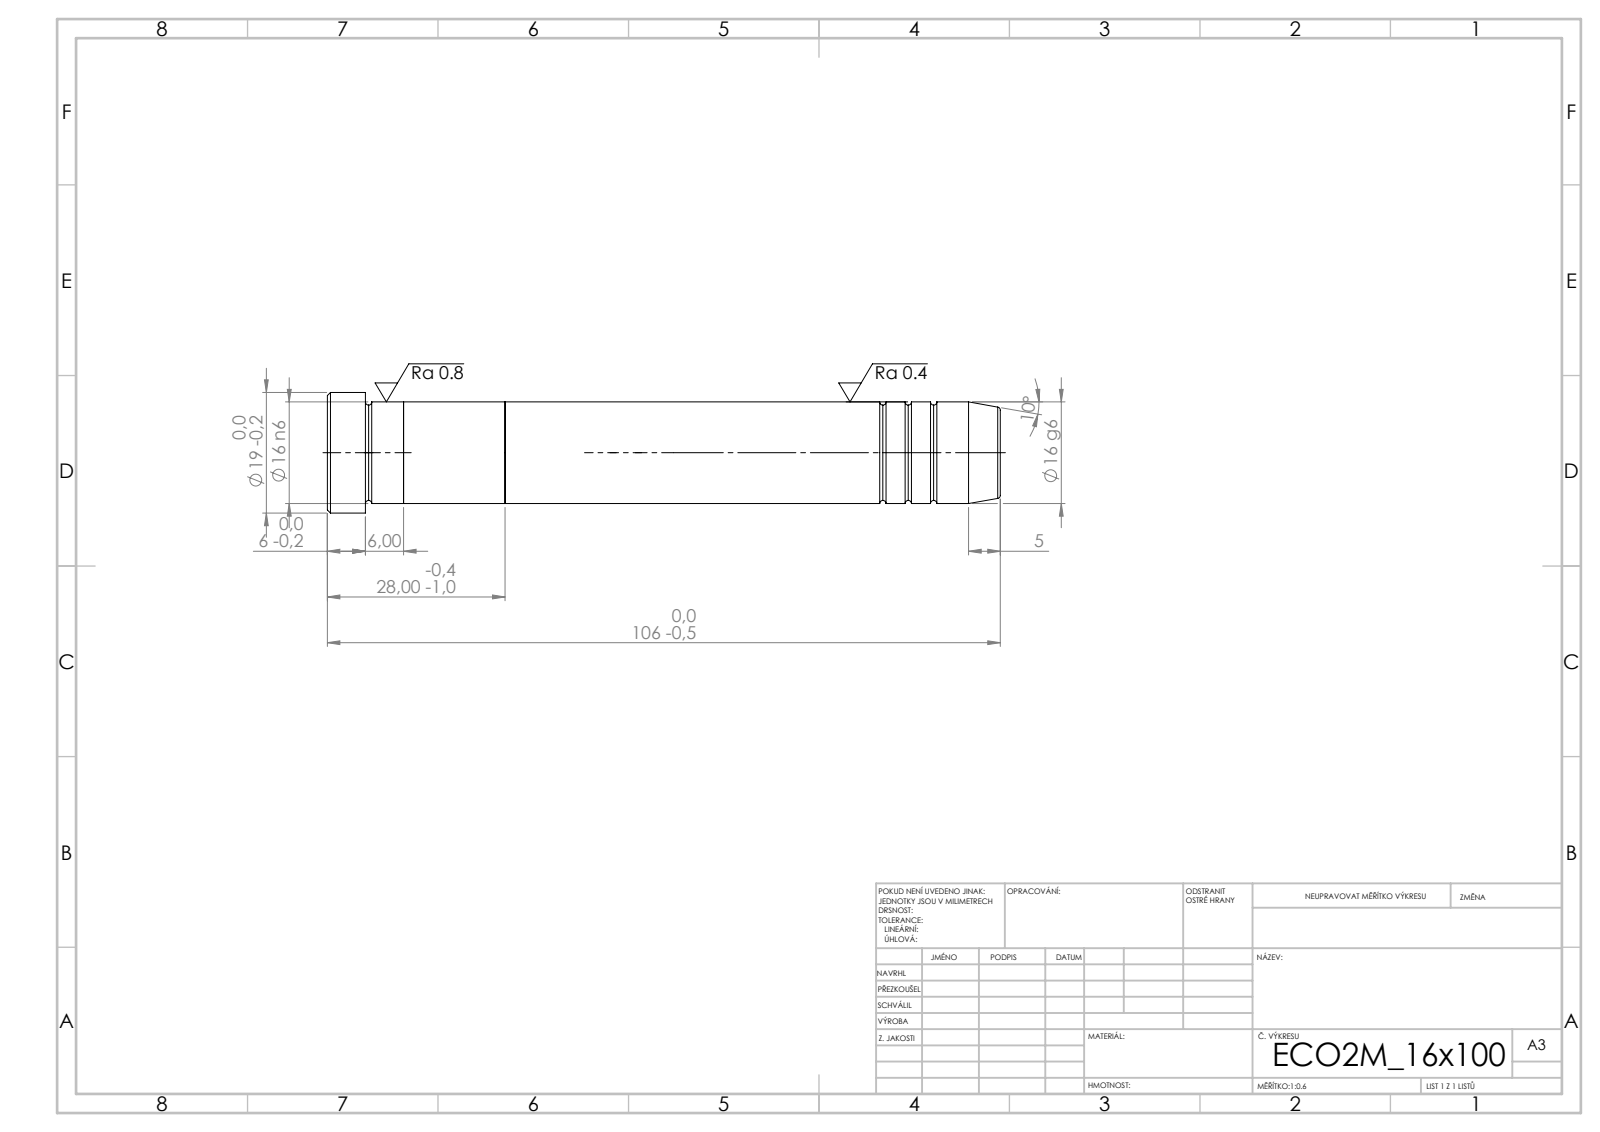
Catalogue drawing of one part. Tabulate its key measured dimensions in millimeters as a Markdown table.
| quantity | value |
| --- | --- |
| STEP written by | SolidWorks 2019 (CONFIG_CONTROL_DESIGN) |
| units | millimeters |
| bodies | 3 solids, 43 faces (7 planar, 14 cylindrical, 22 other) |
| overall size | 106 × 19 × 19 |
| volume | 21 615 mm³ |
| surface area | 6 782 mm² |
| round bosses / shafts (diameter × count) | 19 × 1, 16 × 1 |
| main face-to-face distances | 16, 28, 12, 6, 78, 94, 106, 100, 22 |
